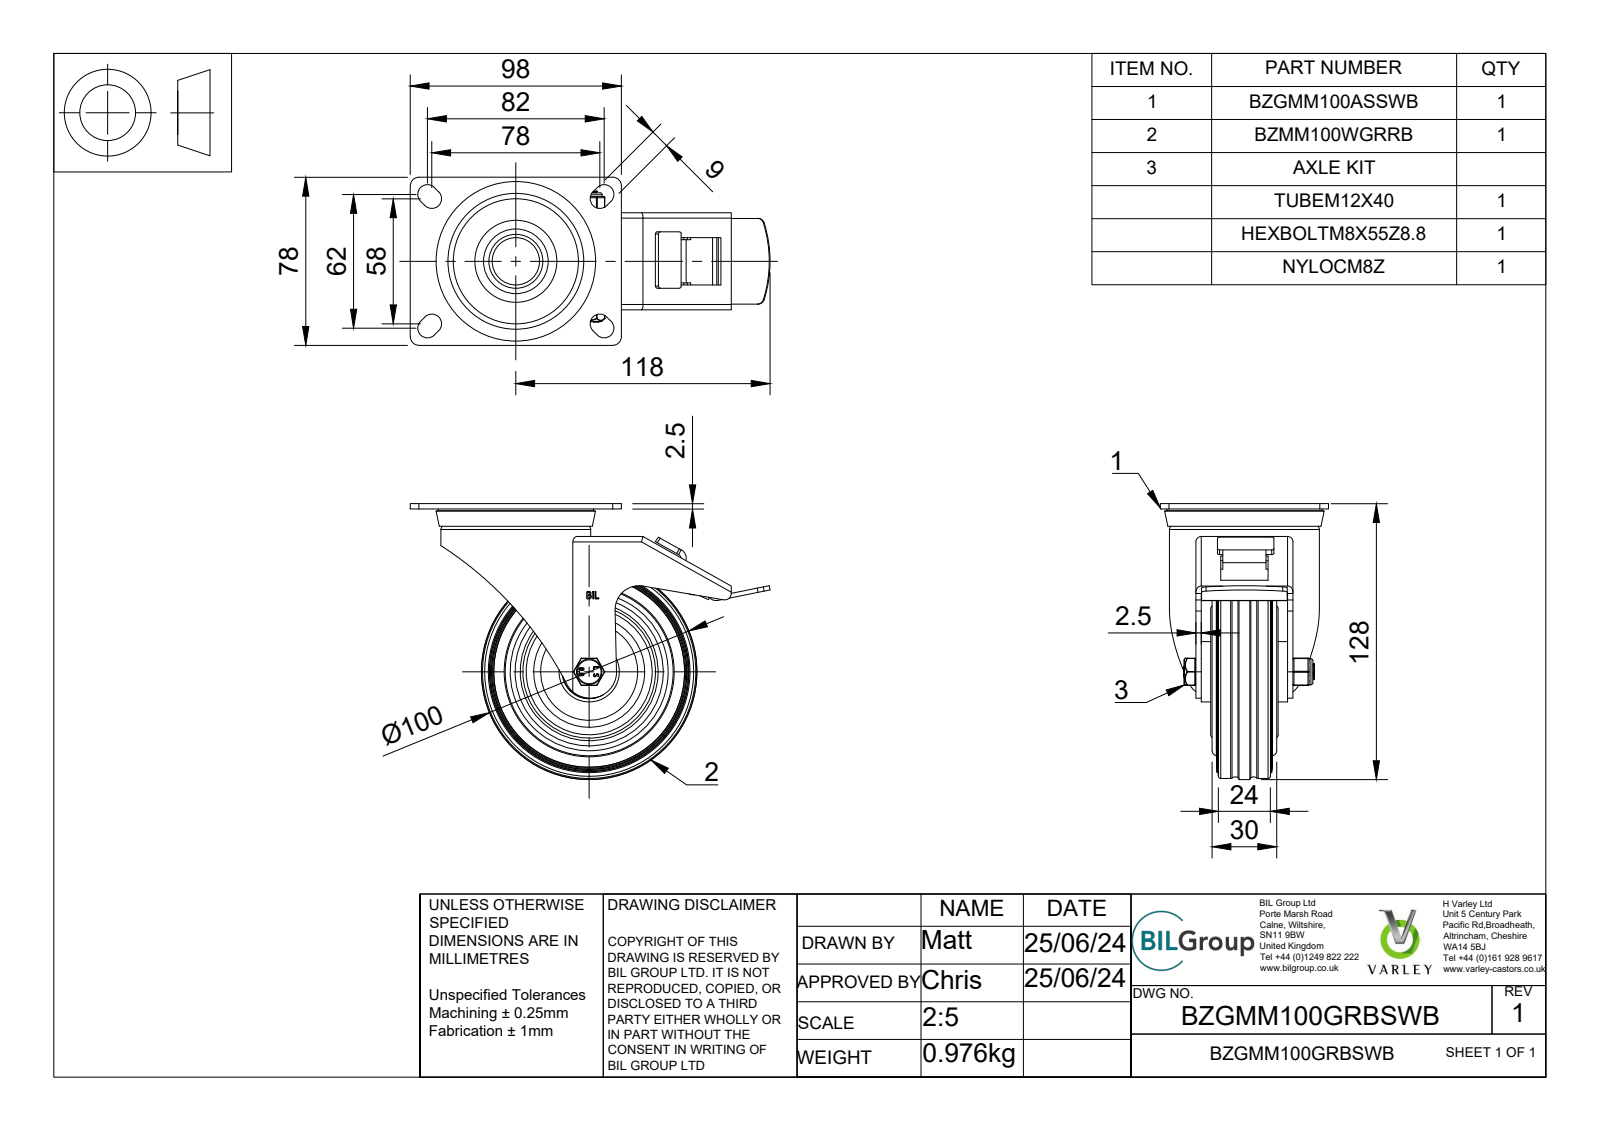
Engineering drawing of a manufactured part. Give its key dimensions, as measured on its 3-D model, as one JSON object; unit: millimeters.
{"part_name": "BZGMM100GRBSWB v3; BZGMM100ASSWB - 2 v1; ZINC PLATED, PRESSED STEEL FORKS; BRAKE PAD (+7 more)", "step_written_by": "Autodesk Translation Framework v13.14.0.145 (AUTOMOTIVE_DESIGN)", "units": "millimeters", "bodies": {"solids": 49, "faces": 655, "planar": 268, "cylindrical": 196, "other": 191}, "overall_size": [167, 128, 78], "volume_mm3": 284335, "surface_area_mm2": 131978, "round_holes": [[0.66, 2], [8, 1], [8.2, 1], [8.4, 1], [8.6, 1], [12, 1], [13, 1], [22, 1], [25, 1], [26, 1], [30, 1], [50.79, 1]], "round_bosses_or_shafts": [[4.5, 8], [100, 1], [99, 1], [69.5, 1], [61.5, 1], [47, 1], [28, 1], [25, 1]], "partial_cylinders_radius": [[0.5, 18], [0.25, 12], [1.25, 8], [4.5, 8], [4, 5], [0.33, 4], [0.64, 4], [1, 4]], "face_to_face_distances": [2.5, 3, 42.5, 7.5, 2, 18.75, 15.25, 10, 5.5, 32.62], "hole_center_spacings": [3.22, 2.49]}
